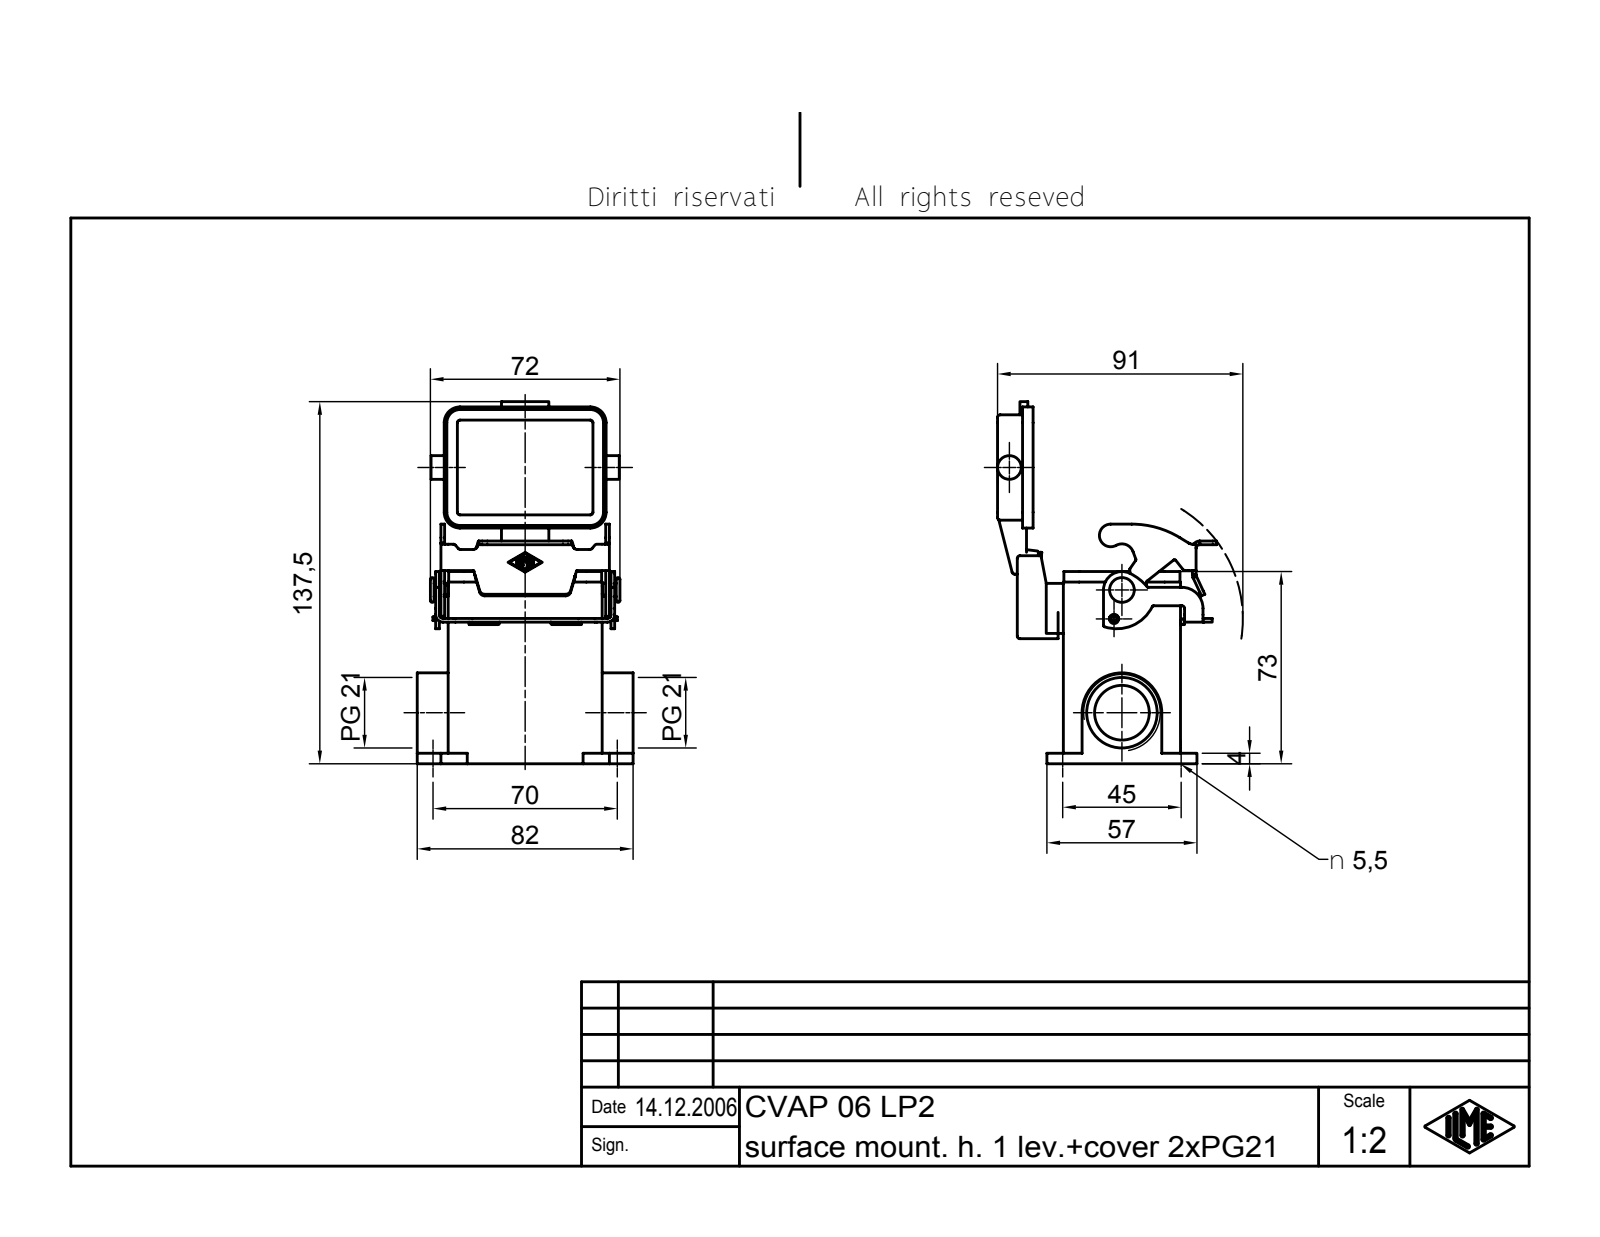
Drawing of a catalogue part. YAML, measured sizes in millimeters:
part_name: "CVAP 06 LP2"
step_written_by: "Autodesk Inventor 7 (AUTOMOTIVE_DESIGN)"
units: millimeters
bodies: {solids: 4, faces: 590, planar: 232, cylindrical: 193, other: 165}
overall_size: [137.5, 83.23, 82]
volume: 111843
surface_area: 63511
round_holes:
  - {diameter: 5.5, count: 4}
  - {diameter: 3.5, count: 1}
  - {diameter: 4, count: 1}
  - {diameter: 20.78, count: 1}
  - {diameter: 26.78, count: 1}
round_bosses_or_shafts:
  - {diameter: 5, count: 2}
  - {diameter: 9, count: 1}
  - {diameter: 7, count: 1}
  - {diameter: 3.2, count: 1}
  - {diameter: 3, count: 1}
partial_cylinders:
  - {radius: 1, count: 32}
  - {radius: 0.25, count: 15}
  - {radius: 0.5, count: 10}
  - {radius: 1.5, count: 9}
  - {radius: 6, count: 8}
  - {radius: 2, count: 7}
  - {radius: 1.4, count: 6}
  - {radius: 2.8, count: 6}
face_to_face_distances: [4, 40.5, 44.5, 2, 10.75, 36.5, 47.75, 69.5, 65.5, 13.5]
hole_center_spacings: [45, 70, 83.22, 35.74]
